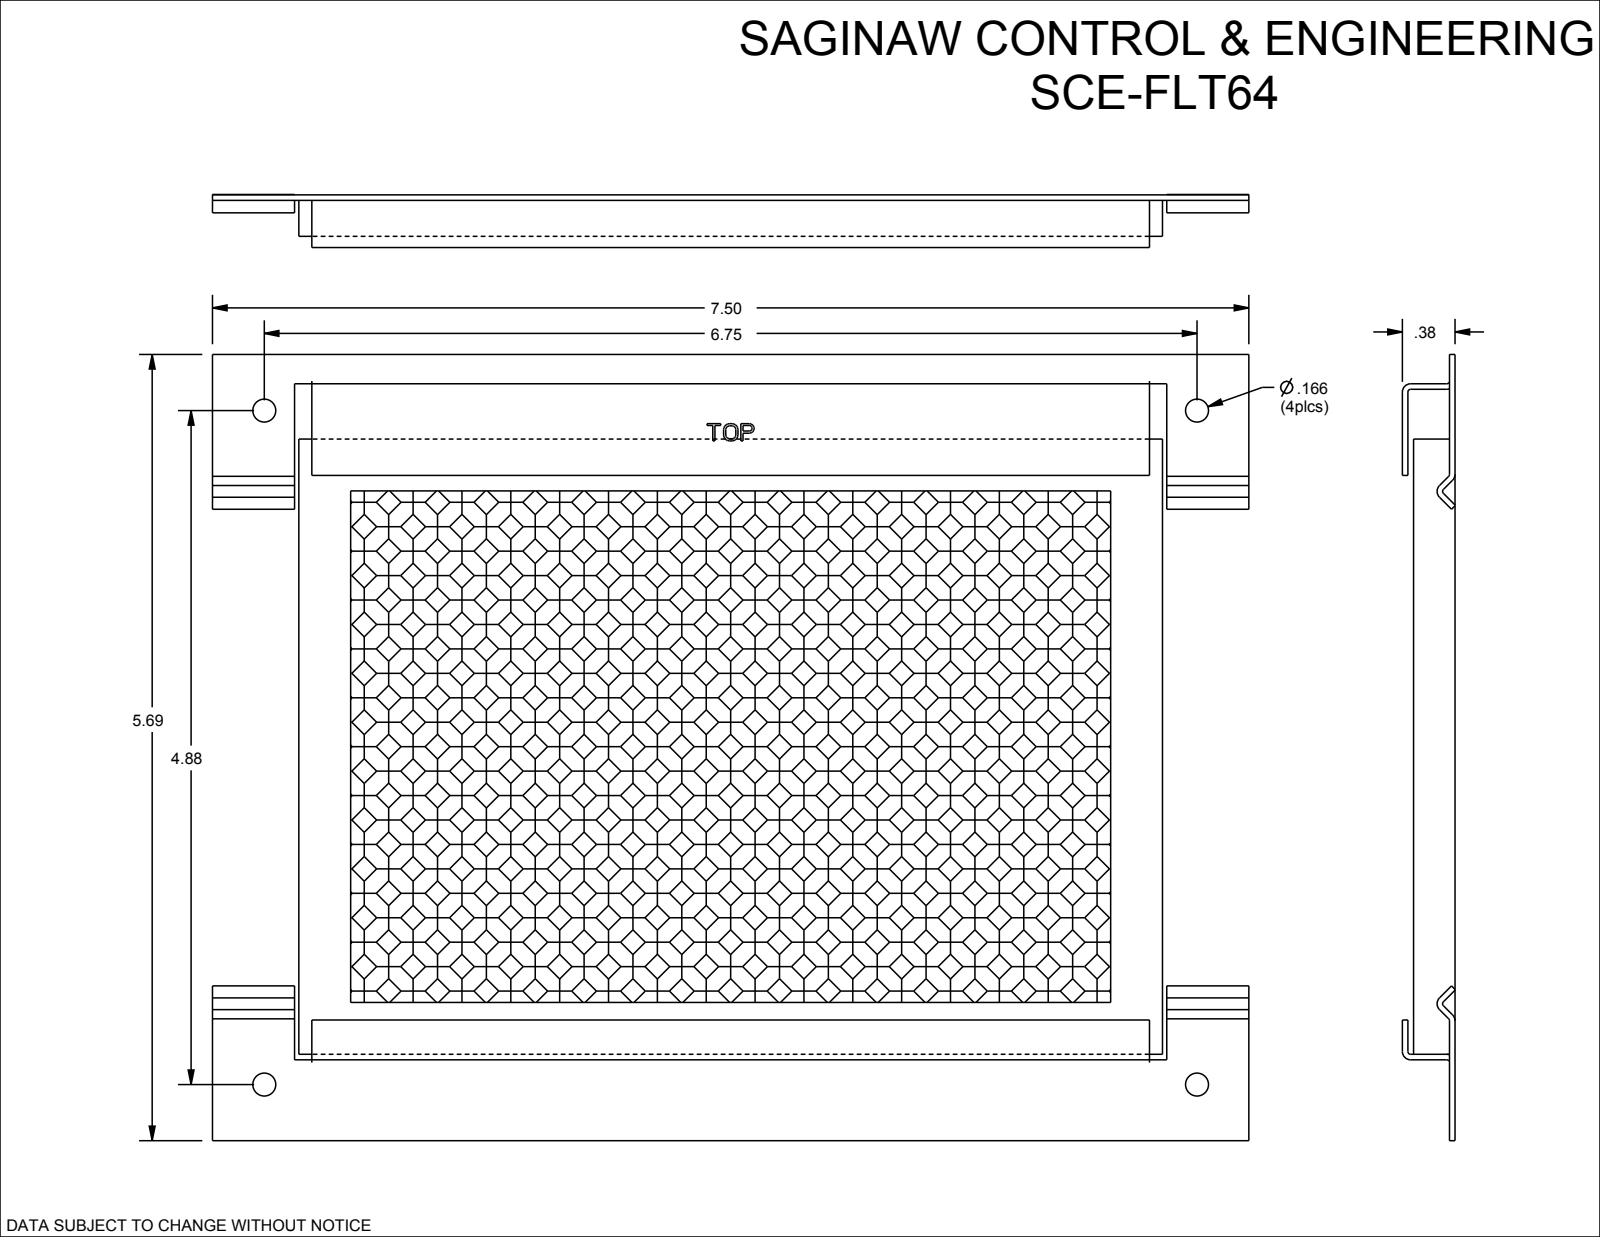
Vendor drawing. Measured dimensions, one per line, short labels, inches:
name: SCE-FLT64
written by: SolidWorks 2019 (CONFIG_CONTROL_DESIGN)
unit: in
bodies: 3 solids, 2200 faces (764 planar, 1436 cylindrical, 0 other)
size: 7.5 × 5.687 × 0.384
volume: 4.605 in³; area: 112 in²
holes: 4× ⌀0.166
bosses: 33× ⌀0.125, 19× ⌀0.125
rounds: 8× R0.02, 8× R0.06
face distances: 0.04, 0.3, 0.26, 0.04, 0.16, 0.1, 0.14, 0.14, 0.02, 0.12
hole spacings: 4.875, 6.75, 6.75, 8.326, 8.326
